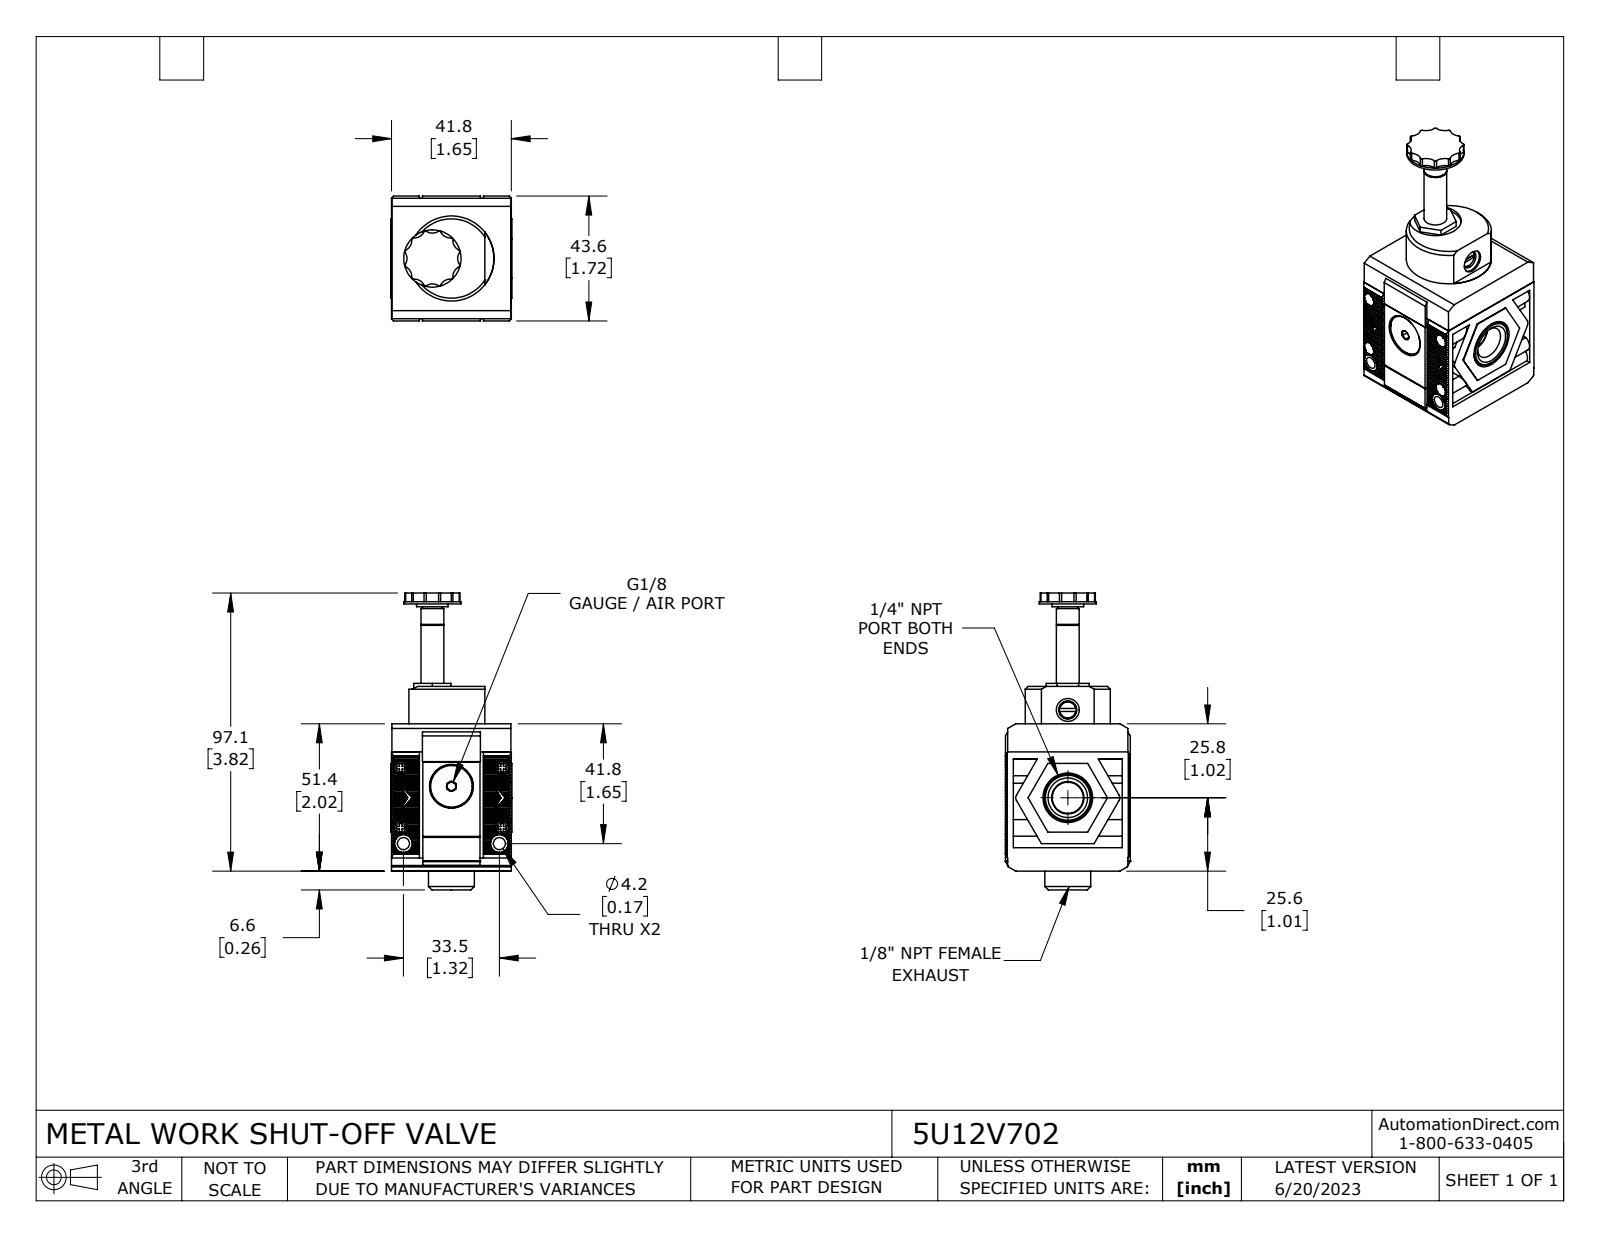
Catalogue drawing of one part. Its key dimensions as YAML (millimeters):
part_name: "5U12V702"
step_written_by: "SolidWorks 2021 (CONFIG_CONTROL_DESIGN)"
units: millimeters
bodies: {solids: 13, faces: 1182, planar: 809, cylindrical: 236, other: 137}
overall_size: [103.7, 43.6, 42.2]
volume: 98800
surface_area: 35260
round_holes:
  - {diameter: 2.1, count: 4}
  - {diameter: 3, count: 4}
  - {diameter: 4.7, count: 4}
  - {diameter: 4.2, count: 2}
  - {diameter: 8.6, count: 2}
  - {diameter: 6.3, count: 1}
  - {diameter: 8, count: 1}
  - {diameter: 15.3, count: 1}
  - {diameter: 29.7, count: 1}
  - {diameter: 31.3, count: 1}
round_bosses_or_shafts:
  - {diameter: 4.6, count: 4}
  - {diameter: 2.6, count: 4}
  - {diameter: 6.2, count: 2}
  - {diameter: 32, count: 1}
  - {diameter: 22.8, count: 1}
  - {diameter: 20, count: 1}
  - {diameter: 18.2, count: 1}
  - {diameter: 16, count: 1}
partial_cylinders:
  - {radius: 0.5, count: 12}
  - {radius: 3.8, count: 12}
  - {radius: 0.6, count: 4}
  - {radius: 3.1, count: 4}
  - {radius: 0.2, count: 2}
  - {radius: 2, count: 2}
  - {radius: 9, count: 1}
face_to_face_distances: [41.6, 34, 41.7, 7.8, 42.5, 1.1, 0.8, 9.8, 42, 41.8]
hole_center_spacings: [5.6, 18.8, 20.9, 22.9, 26.1, 26.5, 34.9, 35.4]
